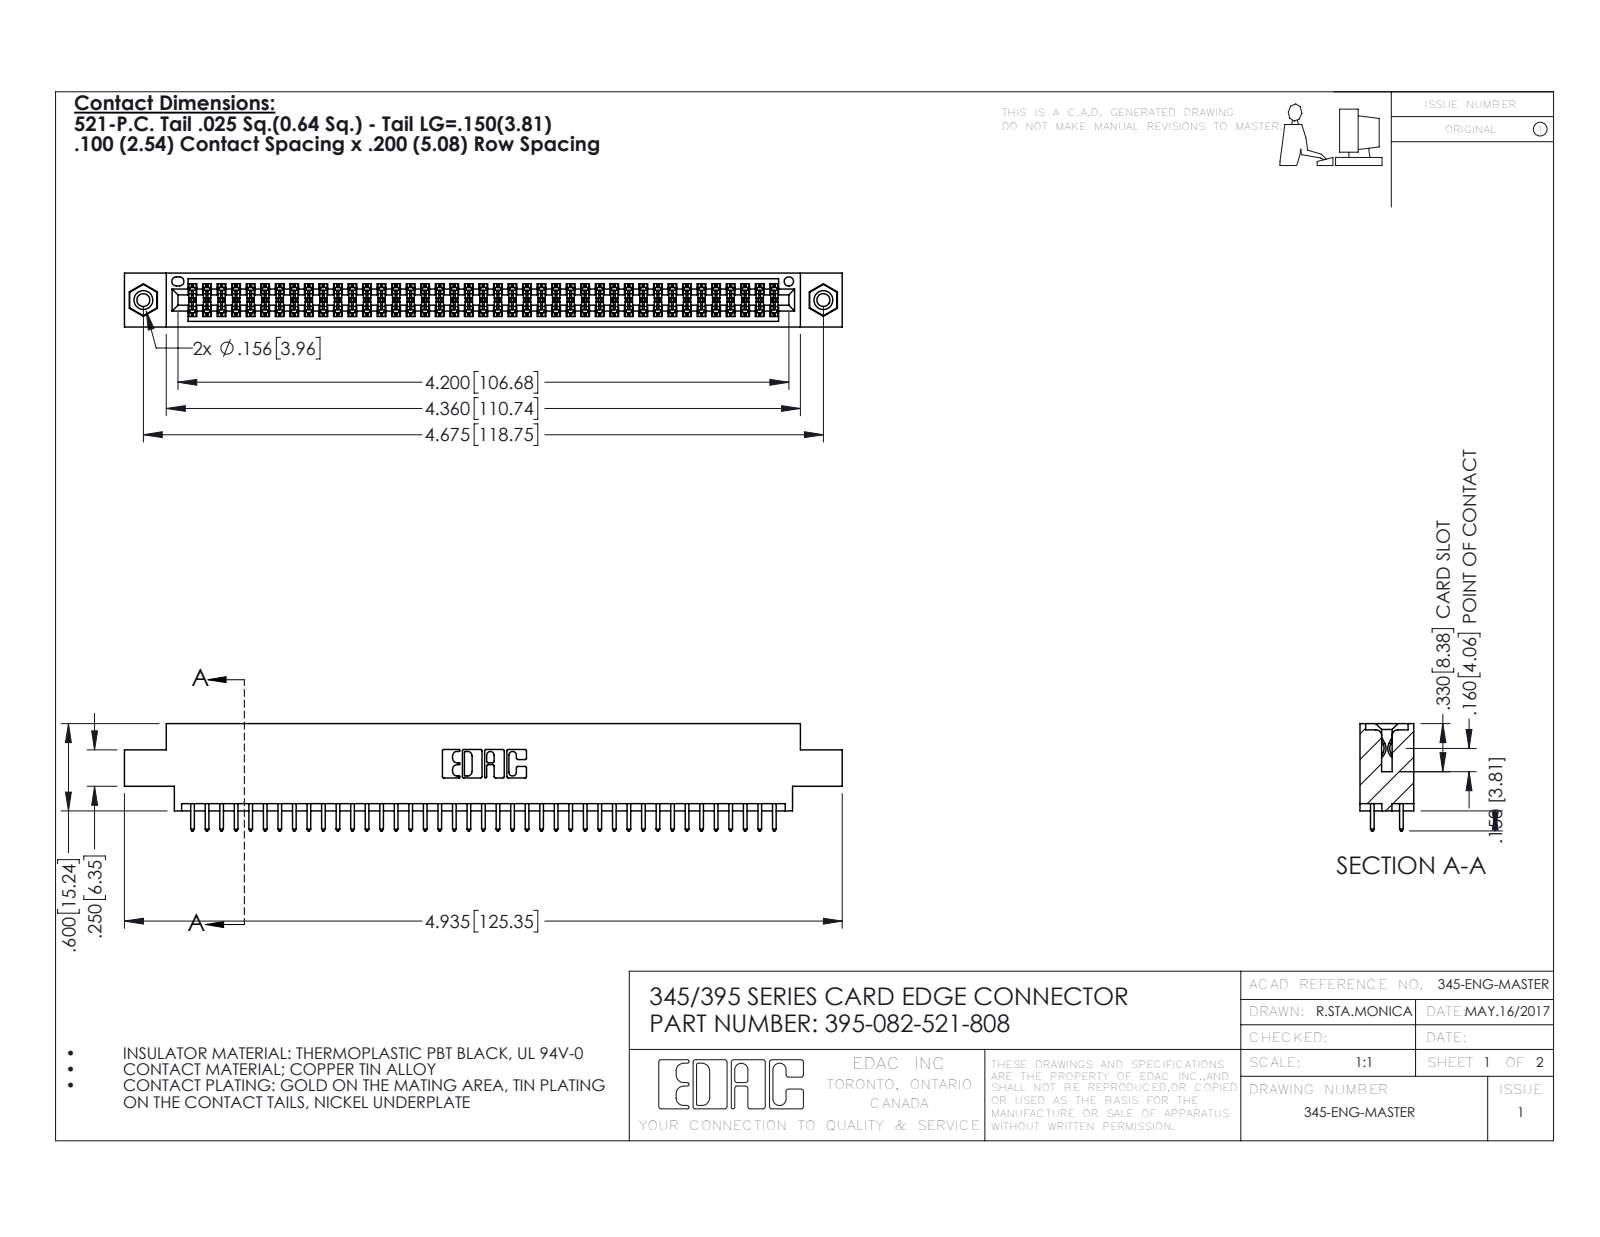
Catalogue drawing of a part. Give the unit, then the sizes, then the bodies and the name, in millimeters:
Units: millimetres
Overall size (bounding box): 125.3 × 18.7 × 9.4
Round holes (diameter × count): ⌀2.3 ×2, ⌀3.2 ×2, ⌀4 ×2, ⌀1.6 ×1
Round bosses / shafts (diameter × count): ⌀3.9 ×2
Partial cylindrical surfaces — rounded edges, fillets, slot ends (radius × count): R0.2 ×123, R0.3 ×82, R0.3 ×22, R0.2 ×6, R0.8 ×6, R0.7 ×3, R0.4 ×2, R0.5 ×2
Main face-to-face distances: 1.8, 7.6, 9.4, 5.1, 2.5, 6.9, 0.6, 5.7, 4.4, 3.8
Hole centre spacings: 6.9, 112.8, 118.7
Volume: 12 000 mm³ · Surface area: 17 680 mm²
Bodies: 85 solids, 4290 faces (2822 planar, 1452 cylindrical, 16 other)
Part name (STEP PRODUCT): 345 Part_0.170 Offset - 0.156 Dia-TI; 395-082-521-808; 345-250-001_345-250-003-102; 345-292-001_345-293-121
STEP written by: SolidWorks 2016 (CONFIG_CONTROL_DESIGN)
